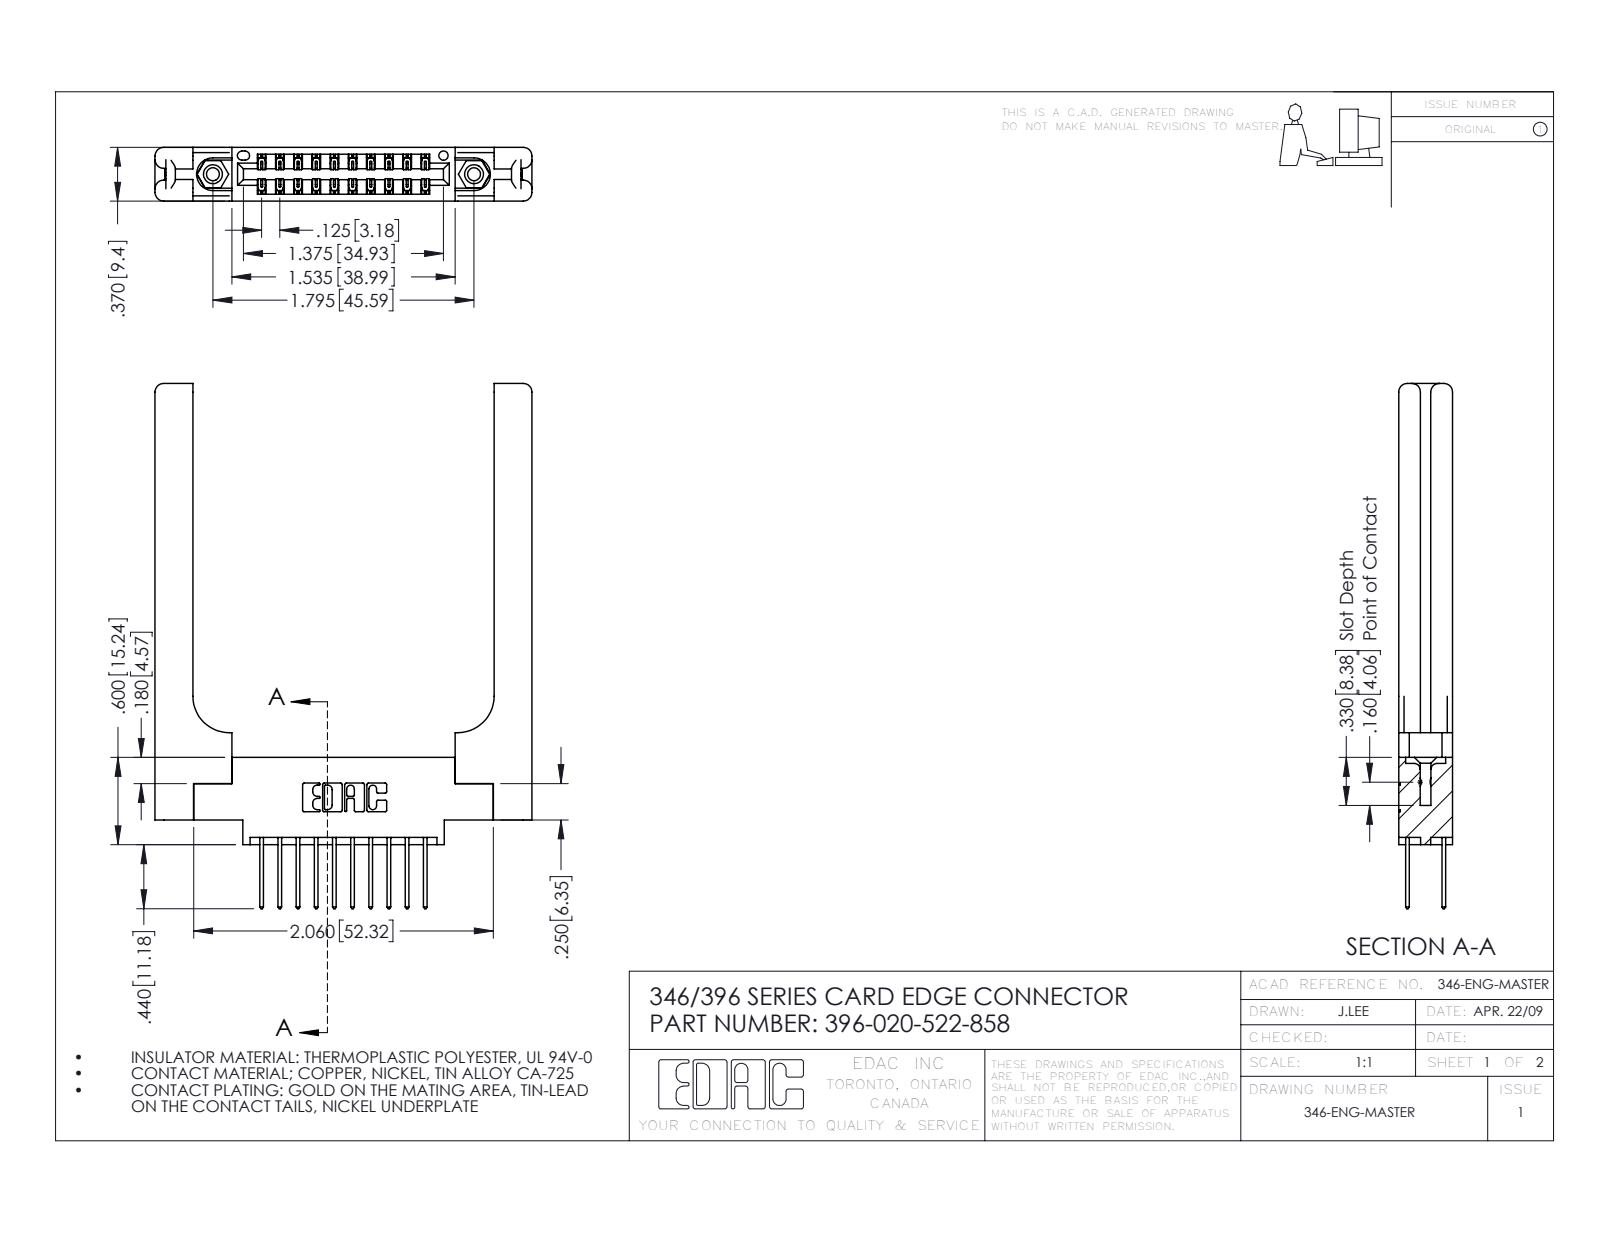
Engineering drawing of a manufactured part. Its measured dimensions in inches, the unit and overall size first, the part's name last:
Units: inches
Overall size (bounding box): 3.61 × 2.591 × 0.37
Round holes (diameter × count): ⌀0.089 ×2, ⌀0.125 ×2, ⌀0.156 ×2, ⌀0.064 ×1
Round bosses / shafts (diameter × count): ⌀0.155 ×2
Partial cylindrical surfaces — rounded edges, fillets, slot ends (radius × count): R0.006 ×30, R0.01 ×22, R0.01 ×20, R0.06 ×16, R0.007 ×6, R0.031 ×6, R0.026 ×3, R0.014 ×2
Main face-to-face distances: 0.37, 0.15, 0.072, 0.148, 0.048, 0.322, 0.25, 0.102, 0.22, 0.173
Hole centre spacings: 0.246, 1.59, 1.795
Volume: 0.827 in³ · Surface area: 20.5 in²
Bodies: 25 solids, 1422 faces (928 planar, 434 cylindrical, 60 other)
Part name (STEP PRODUCT): 345-250-001_345-250-001-102; 346 Part_0.170 Offset - 0.156 Dia-TH; 396-020-522-858; 346-220-058_345-220-058 (+1 more)
STEP written by: SolidWorks 2016 (CONFIG_CONTROL_DESIGN)
